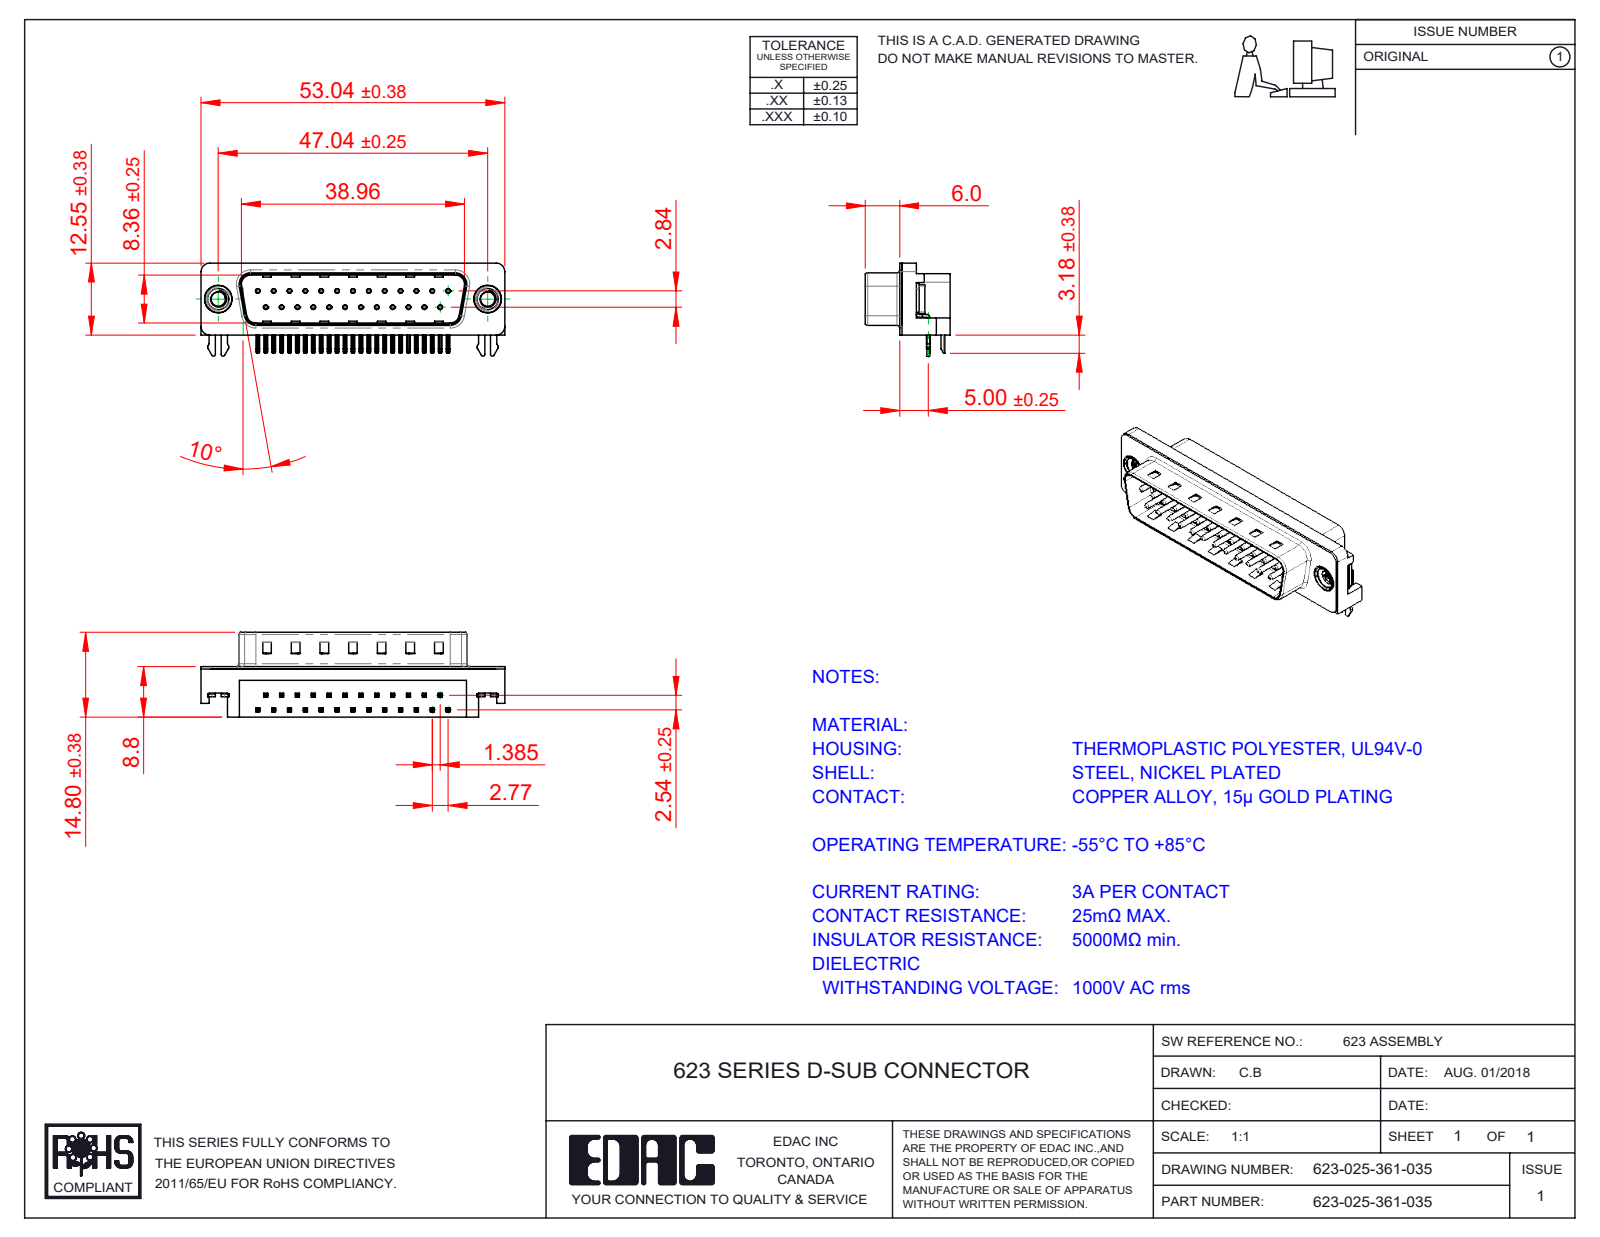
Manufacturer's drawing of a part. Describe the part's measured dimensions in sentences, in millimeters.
The part is named "623 Contact Top; 623-025-361-035; 623 M3 Threaded Rivet; 623 Contact Bottom (+3 more)". Its 3-D file was written by "SolidWorks 2016 (CONFIG_CONTROL_DESIGN)". It is 31 solids with 2285 faces: 1433 planar, 657 cylindrical and 195 other. Overall it measures 53.04 by 16.25 by 14.8 millimeters. Its volume is 4 728 cubic millimeters and its surface area 6 782 square millimeters. Round holes: 25 of diameter 0.35, 25 of diameter 0.8, 2 of diameter 2.5, 2 of diameter 4, 2 of diameter 4.8, 2 of diameter 5. Round bosses or shafts: 25 of diameter 0.75, 2 of diameter 4.9, 2 of diameter 4.75, 2 of diameter 3.9. Partial cylindrical surfaces (rounded edges, fillets, slot ends): 108 of radius 0.25, 50 of radius 0.12, 14 of radius 0.5, 8 of radius 1, 7 of radius 1.5, 4 of radius 0.32, 4 of radius 0.9, 4 of radius 1.6. The main face-to-face distances are 0.4, 8.4, 2.1, 1.7, 8.76, 10.46, 10.86, 10.35, 8.8, 5.9. The hole center spacings are 3.16, 2.77, 11.08, 5.54, 8.31, 5.03, 13.85, 7.48.
